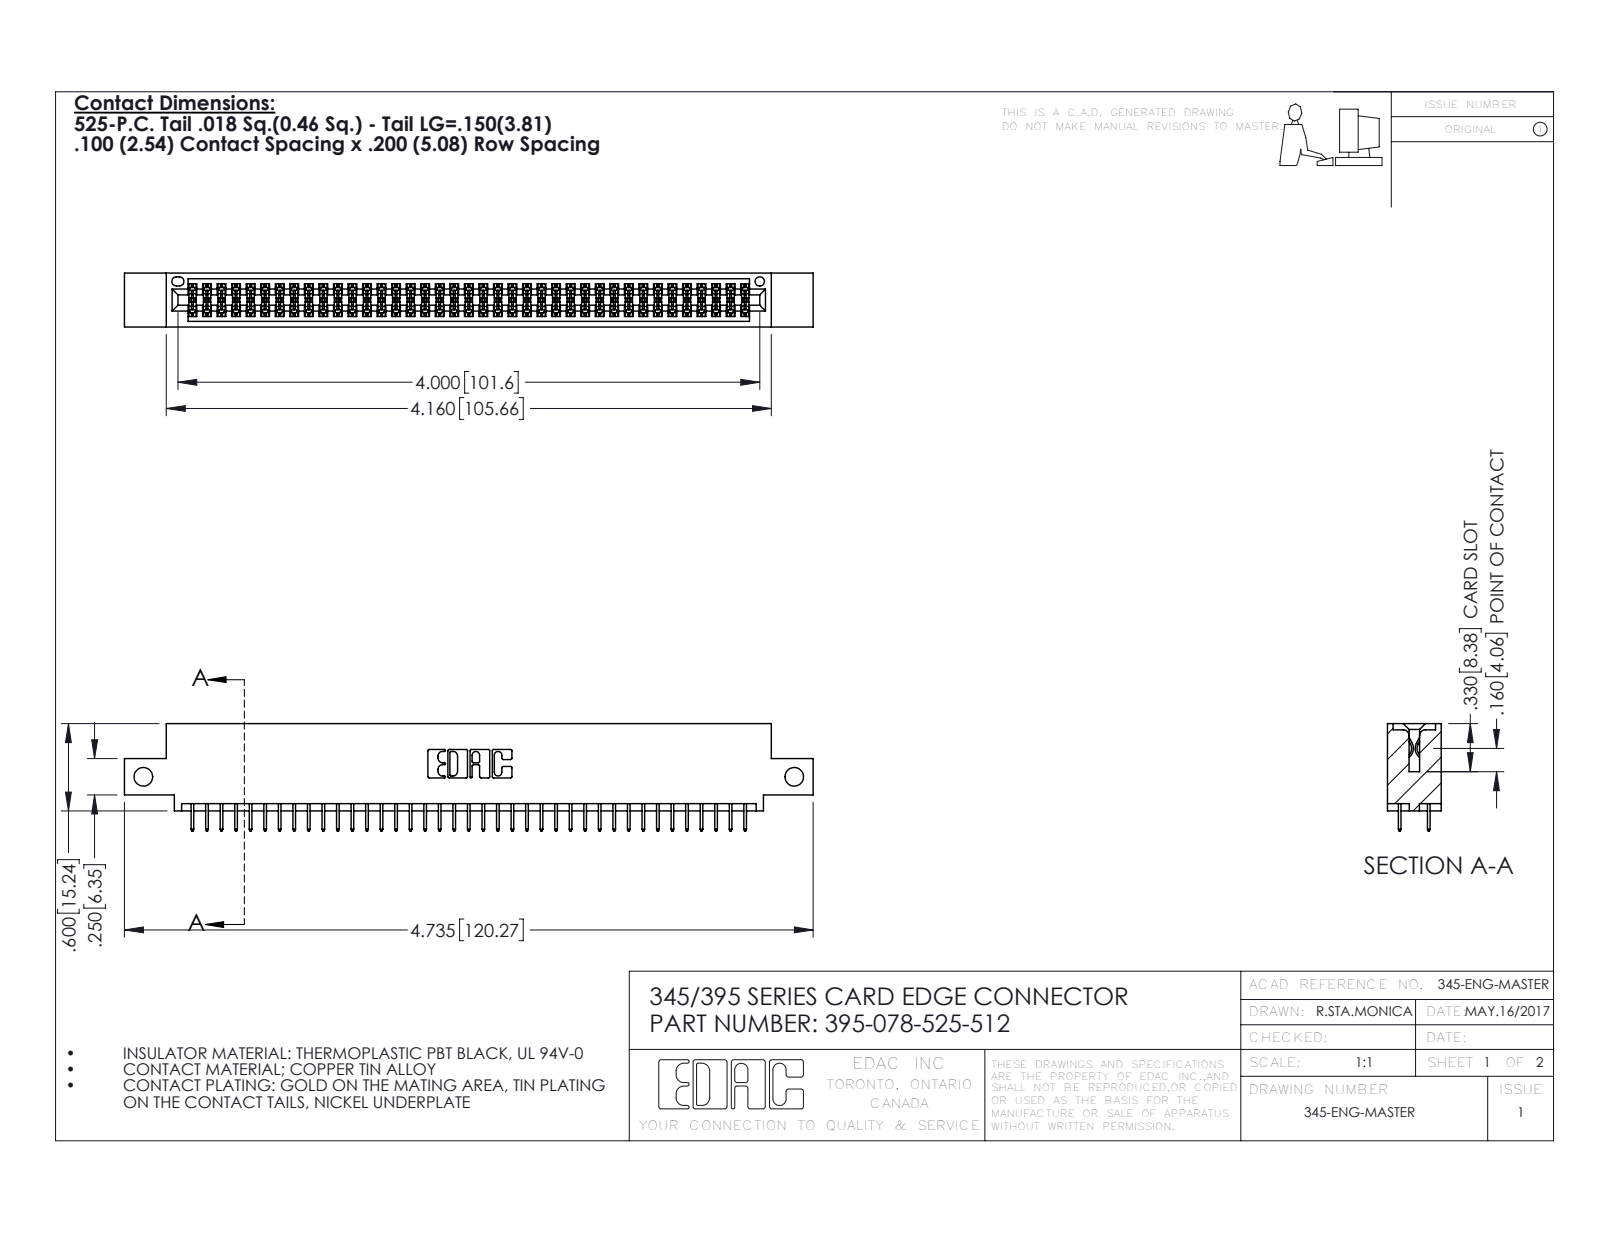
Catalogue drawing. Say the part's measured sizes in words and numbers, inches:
The part is named "345-292-001_345-293-125; 345 Part_0.110 Offset - Side Mount; 395-078-525-512". Its 3-D file was written by "SolidWorks 2020 (CONFIG_CONTROL_DESIGN)". It is 79 solids with 4342 faces: 3126 planar, 1216 cylindrical and 0 other. Overall it measures 4.735 by 0.737 by 0.37 inches. Its volume is 0.694 cubic inches and its surface area 25.29 square inches. Round holes: 2 of diameter 0.128, 1 of diameter 0.064. Partial cylindrical surfaces (rounded edges, fillets, slot ends): 117 of radius 0.006, 22 of radius 0.01, 6 of radius 0.007, 6 of radius 0.031, 3 of radius 0.026, 2 of radius 0.014, 2 of radius 0.019, 2 of radius 0.022. The main face-to-face distances are 0.072, 0.298, 0.2, 0.37, 0.098, 0.272, 0.025, 0.225, 0.072, 0.175. The hole center spacings are 4.475.
